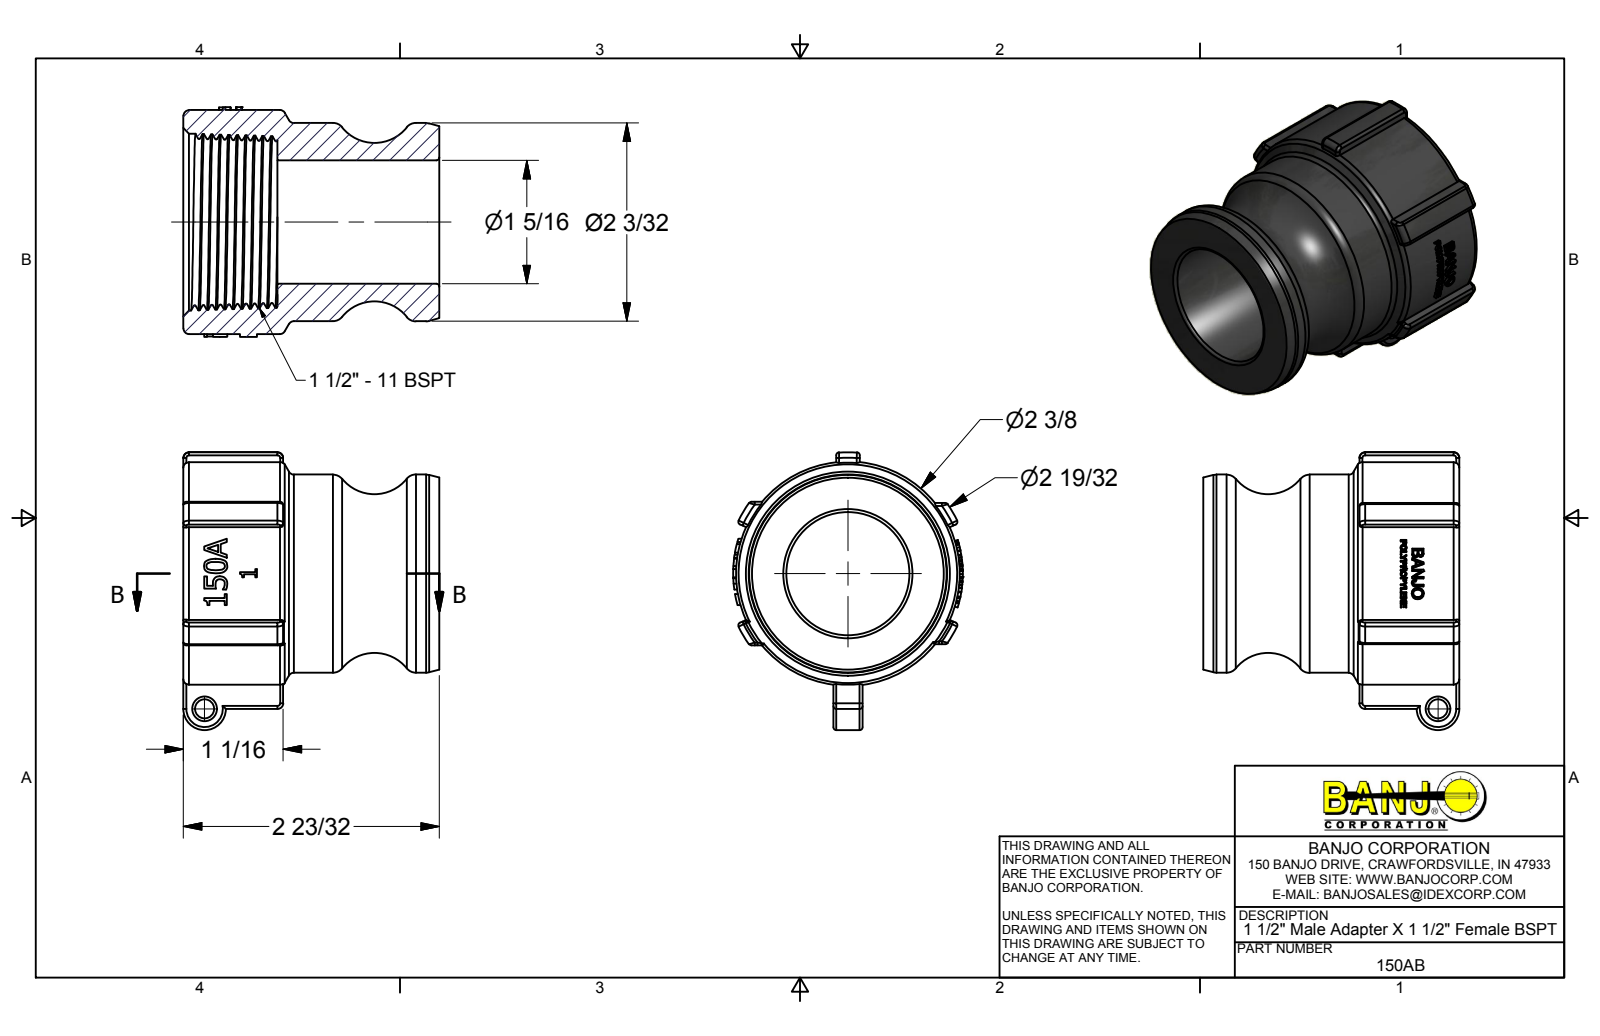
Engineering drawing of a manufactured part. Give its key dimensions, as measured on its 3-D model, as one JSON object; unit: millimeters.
{"part_name": "150AB", "step_written_by": "Autodesk Inventor 2014 (AUTOMOTIVE_DESIGN)", "units": "millimeters", "bodies": {"solids": 1, "faces": 480, "planar": 176, "cylindrical": 88, "other": 216}, "overall_size": [74.98, 69.09, 61.98], "volume_mm3": 84930, "surface_area_mm2": 27330, "round_holes": [[5.08, 1], [33.27, 1]], "round_bosses_or_shafts": [[53.47, 1]], "partial_cylinders_radius": [[0.79, 36], [1.52, 1], [5.71, 1], [30.23, 1], [30.99, 1], [32.77, 1]], "face_to_face_distances": [43.69, 69.09, 25.4, 7.88, 0.33, 38.43, 0.77, 7.11, 17.12, 55.88]}
